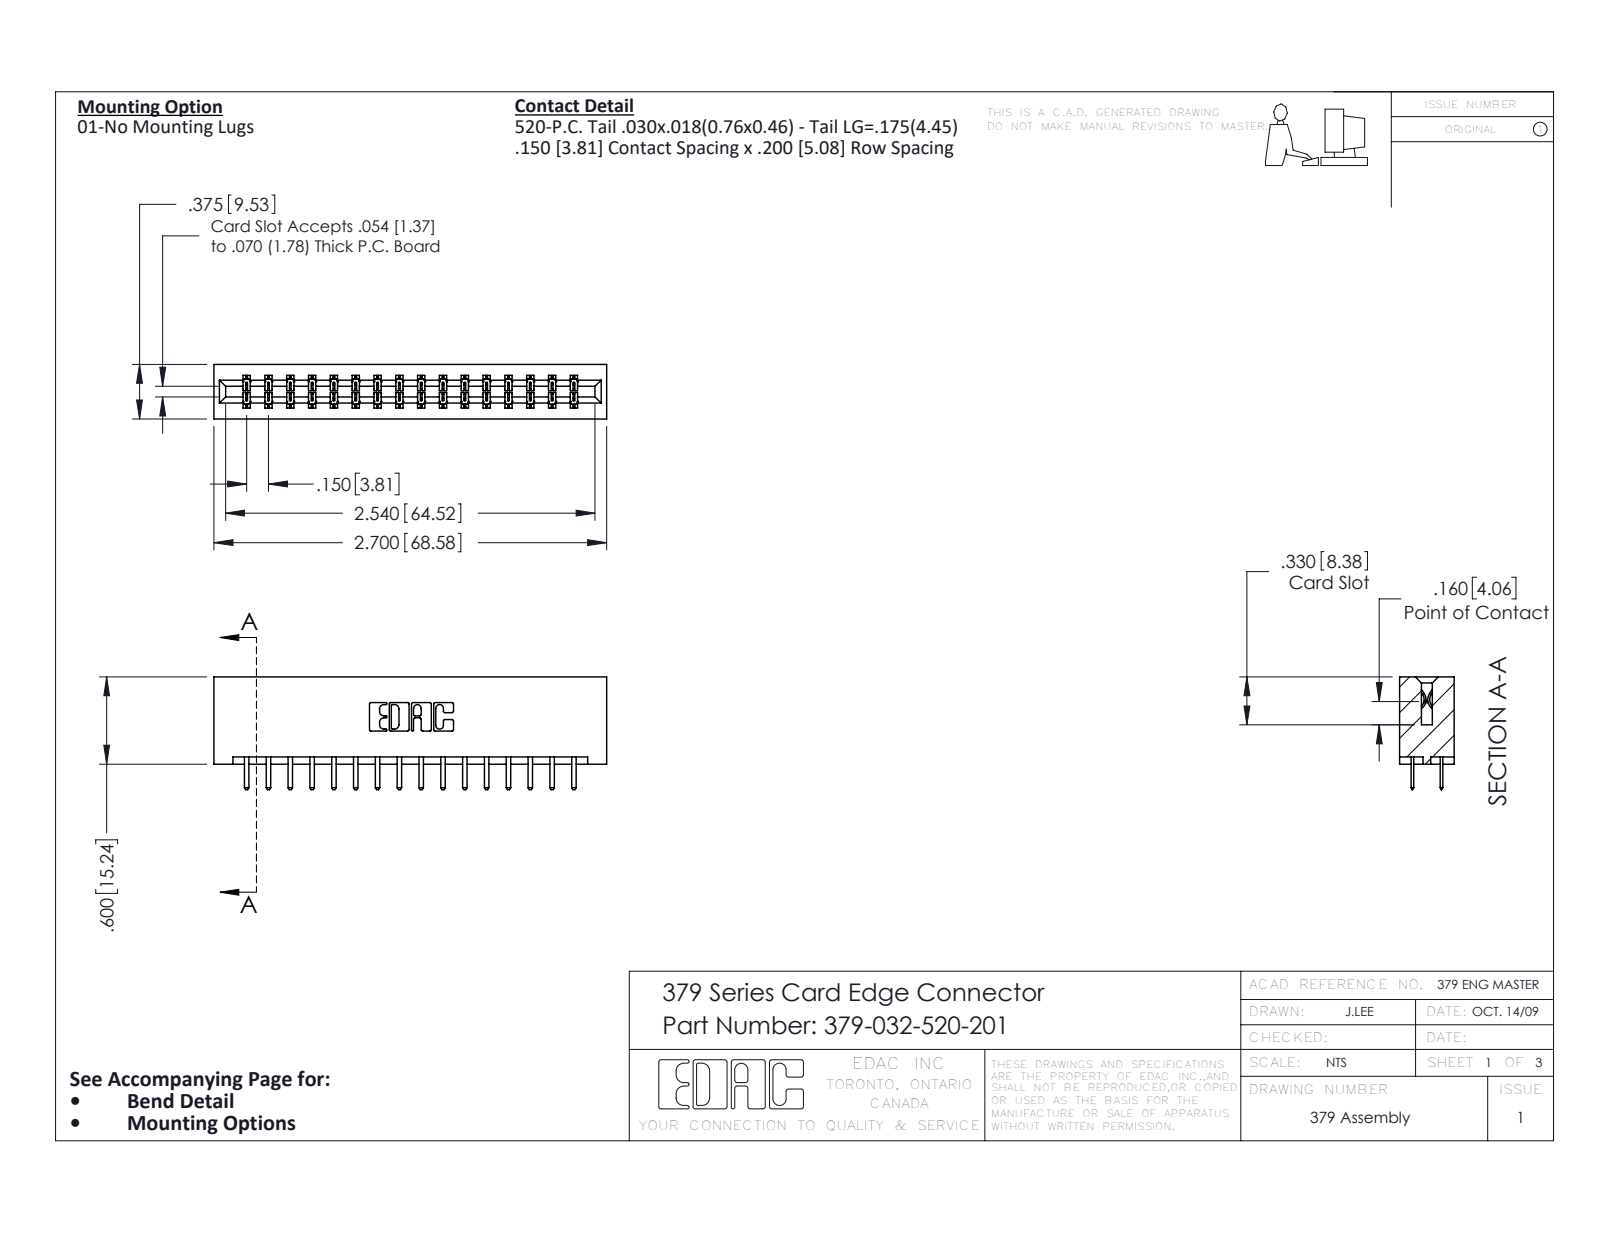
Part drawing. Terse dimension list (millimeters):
name: 379-032-520-201; 345-292-001_345-293-120; 379 Part_Lugless
written by: SolidWorks 2020 (CONFIG_CONTROL_DESIGN)
unit: mm
bodies: 33 solids, 1898 faces (1282 planar, 616 cylindrical, 0 other)
size: 68.6 × 19.7 × 9.5
volume: 7 700 mm³; area: 8 419 mm²
rounds: 48× R0.2, 36× R0.3, 22× R0.3, 6× R0.2, 6× R0.8, 3× R0.7, 2× R0.4, 2× R0.6
face distances: 7.6, 1.9, 5.1, 9.5, 3.8, 2.5, 14, 15.2, 5.7, 1.3
